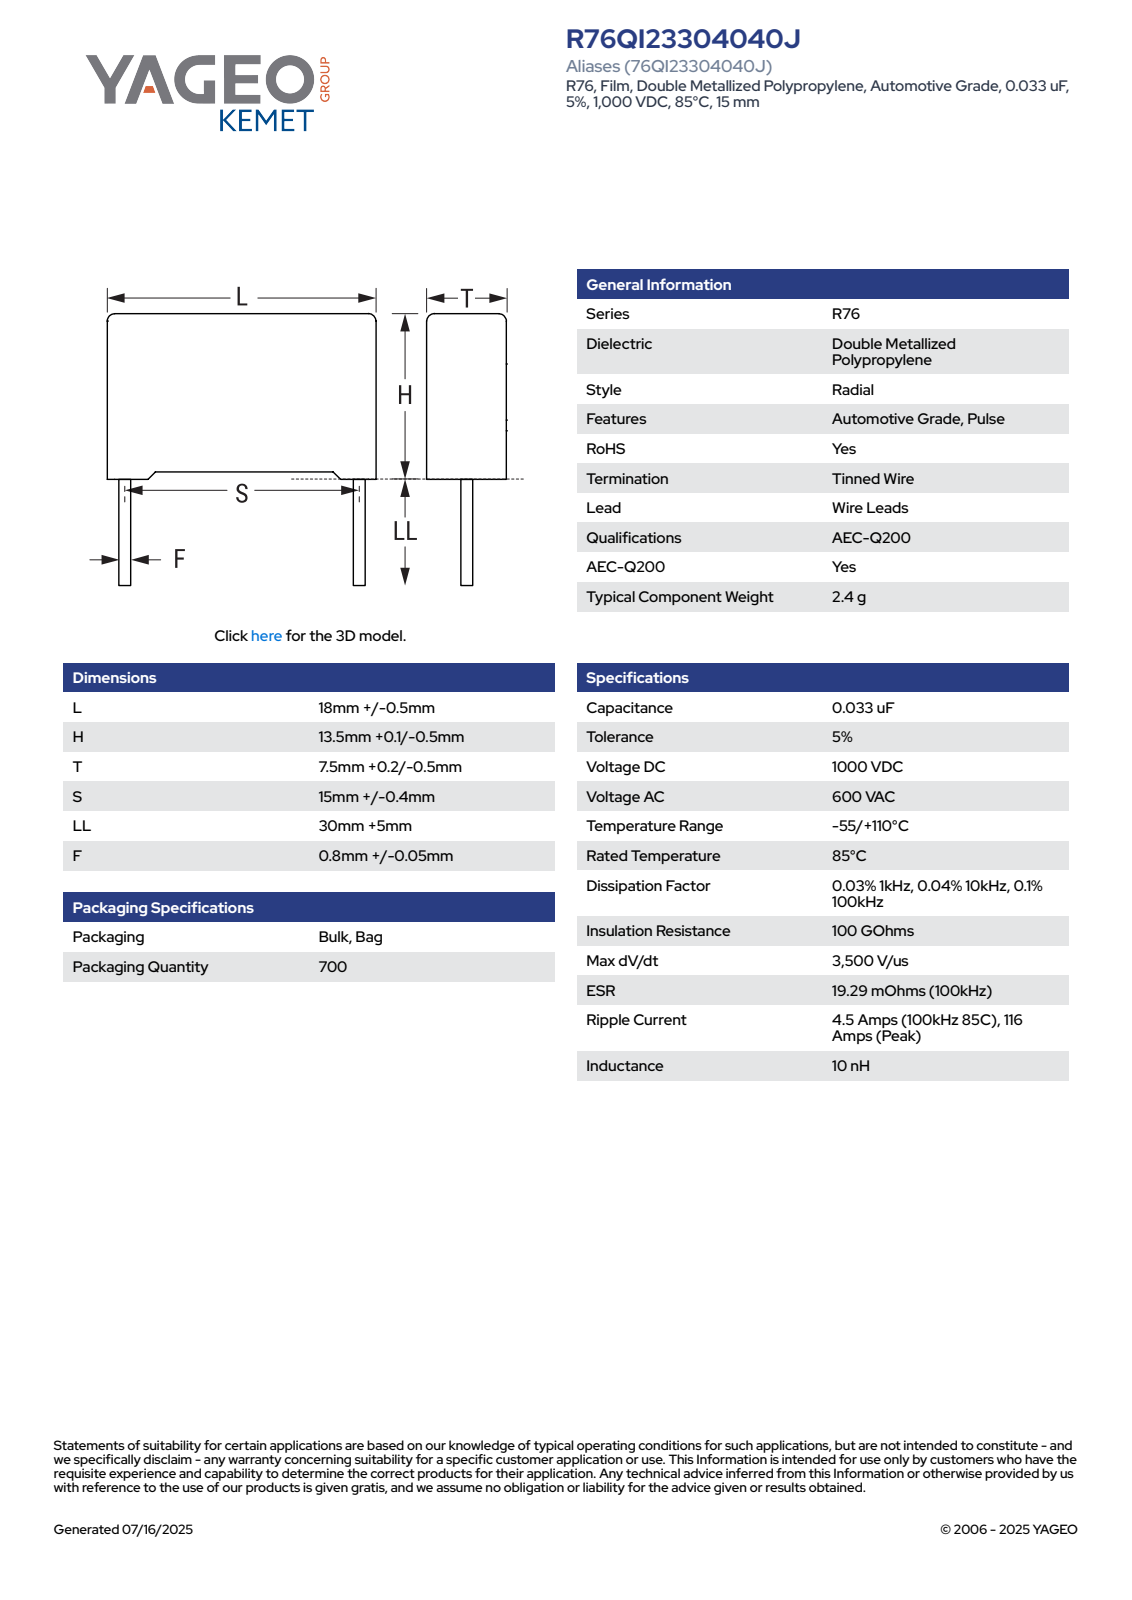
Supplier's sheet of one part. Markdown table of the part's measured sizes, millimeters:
| quantity | value |
| --- | --- |
| part name | CFR_RB2_18X13.5X7.5_L18.5H13.6T7.7S15LL35F0.85 |
| STEP written by | SolidWorks 2021 (AUTOMOTIVE_DESIGN) |
| units | millimeters |
| bodies | 4 solids, 85 faces (77 planar, 8 cylindrical, 0 other) |
| overall size | 48.6 × 18.5 × 7.71 |
| volume | 1 885 mm³ |
| surface area | 1 217 mm² |
| round bosses / shafts (diameter × count) | 0.85 × 2 |
| partial cylindrical surfaces (radius × count) | 0.5 × 4 |
| main face-to-face distances | 7.7, 12.85, 18.5, 0.62, 0.75, 13.6, 7.08, 0.47, 13.13, 17.88 |
